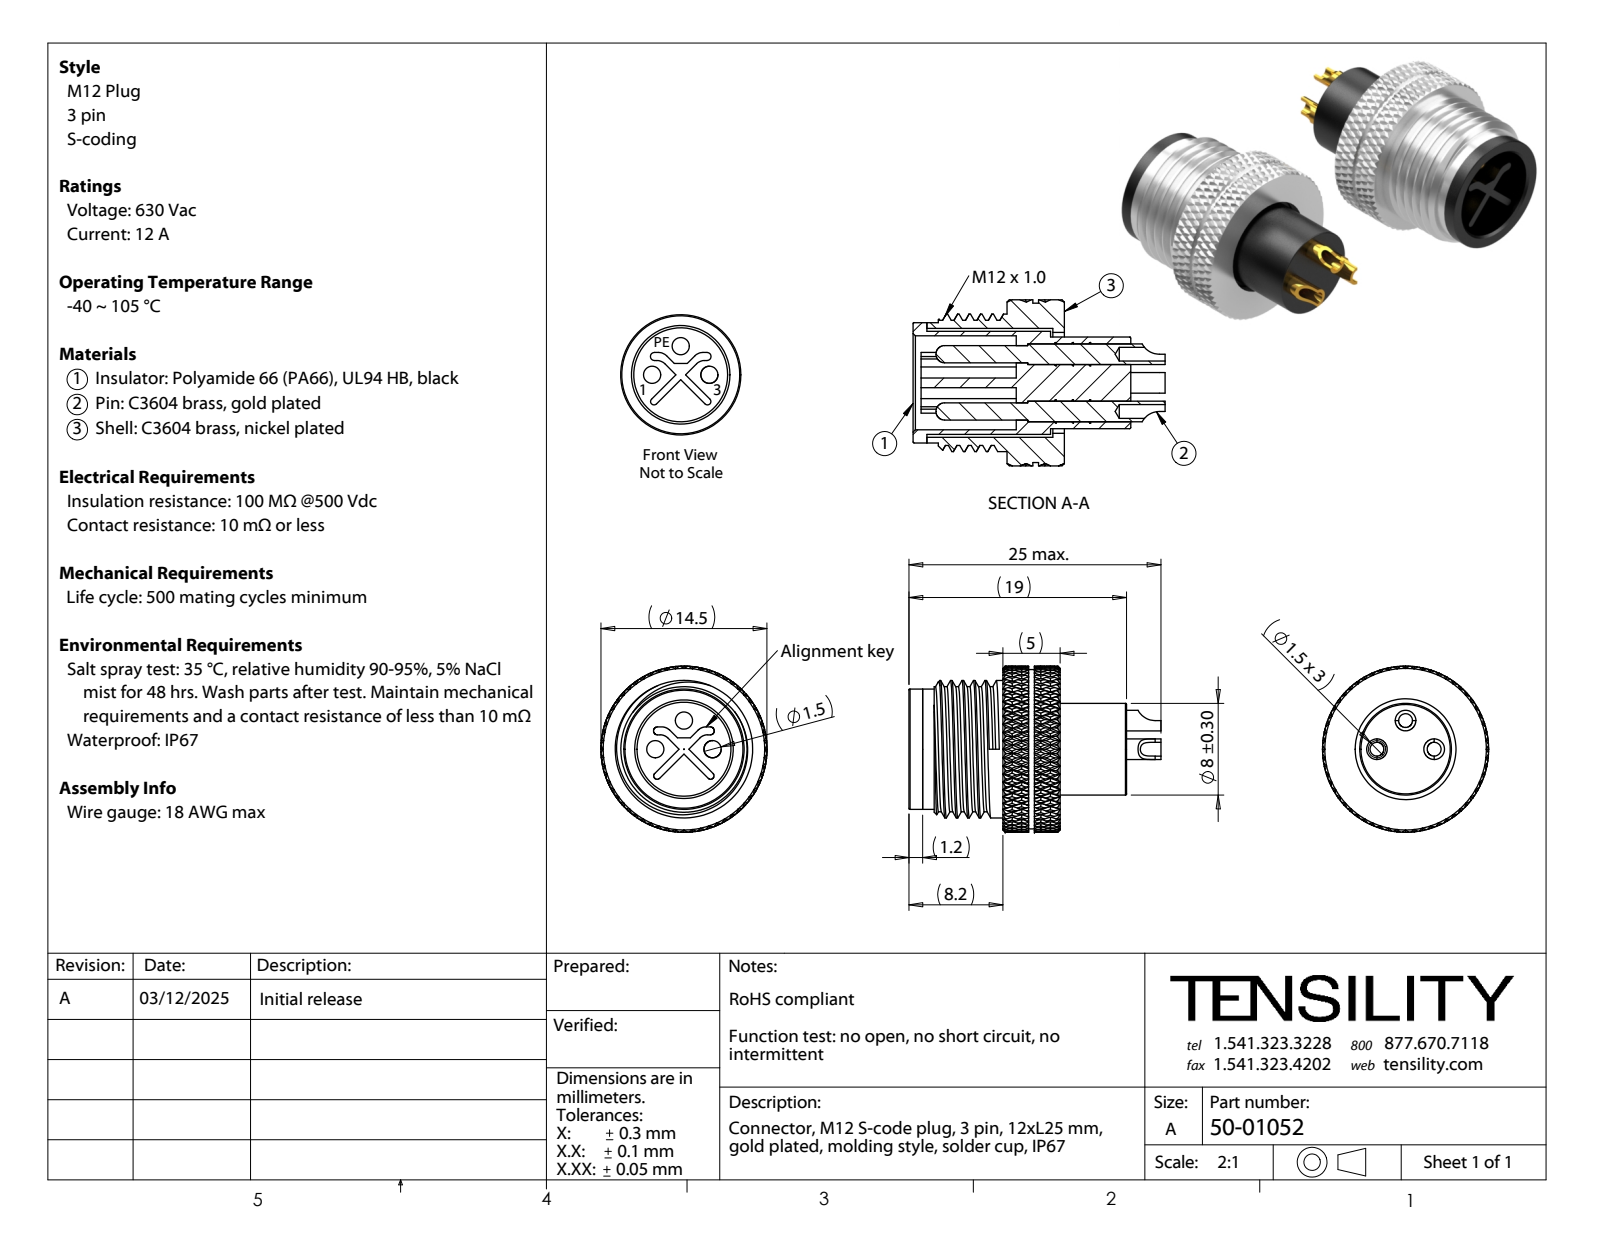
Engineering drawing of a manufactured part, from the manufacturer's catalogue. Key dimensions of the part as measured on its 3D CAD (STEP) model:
Part name (STEP PRODUCT): 50-01052-03; 50-01052-01; 50-01052-02_Step; 50-01052 (+1 more)
STEP written by: SolidWorks 2021 (CONFIG_CONTROL_DESIGN)
Units: millimetres
Bodies: 5 solids, 195 faces (51 planar, 92 cylindrical, 52 other)
Overall size (bounding box): 22 × 14.5 × 14.5
Volume: 1 460 mm³ · Surface area: 2 813 mm²
Round holes (diameter × count): ⌀1.2 ×3, ⌀1.5 ×3, ⌀8.2 ×1, ⌀8.8 ×1, ⌀9.5 ×1
Round bosses / shafts (diameter × count): ⌀1.8 ×3, ⌀14.5 ×1, ⌀13.9 ×1, ⌀12 ×1, ⌀10.5 ×1, ⌀9 ×1, ⌀8 ×1
Partial cylindrical surfaces — rounded edges, fillets, slot ends (radius × count): R1 ×4, R1.7 ×3, R0.3 ×2, R0.35 ×2
Main face-to-face distances: 0.6, 12, 10.8, 10, 7, 5, 5.8, 7.8, 0.8, 4.2
Hole centre spacings: 2.5, 3.54, 5
